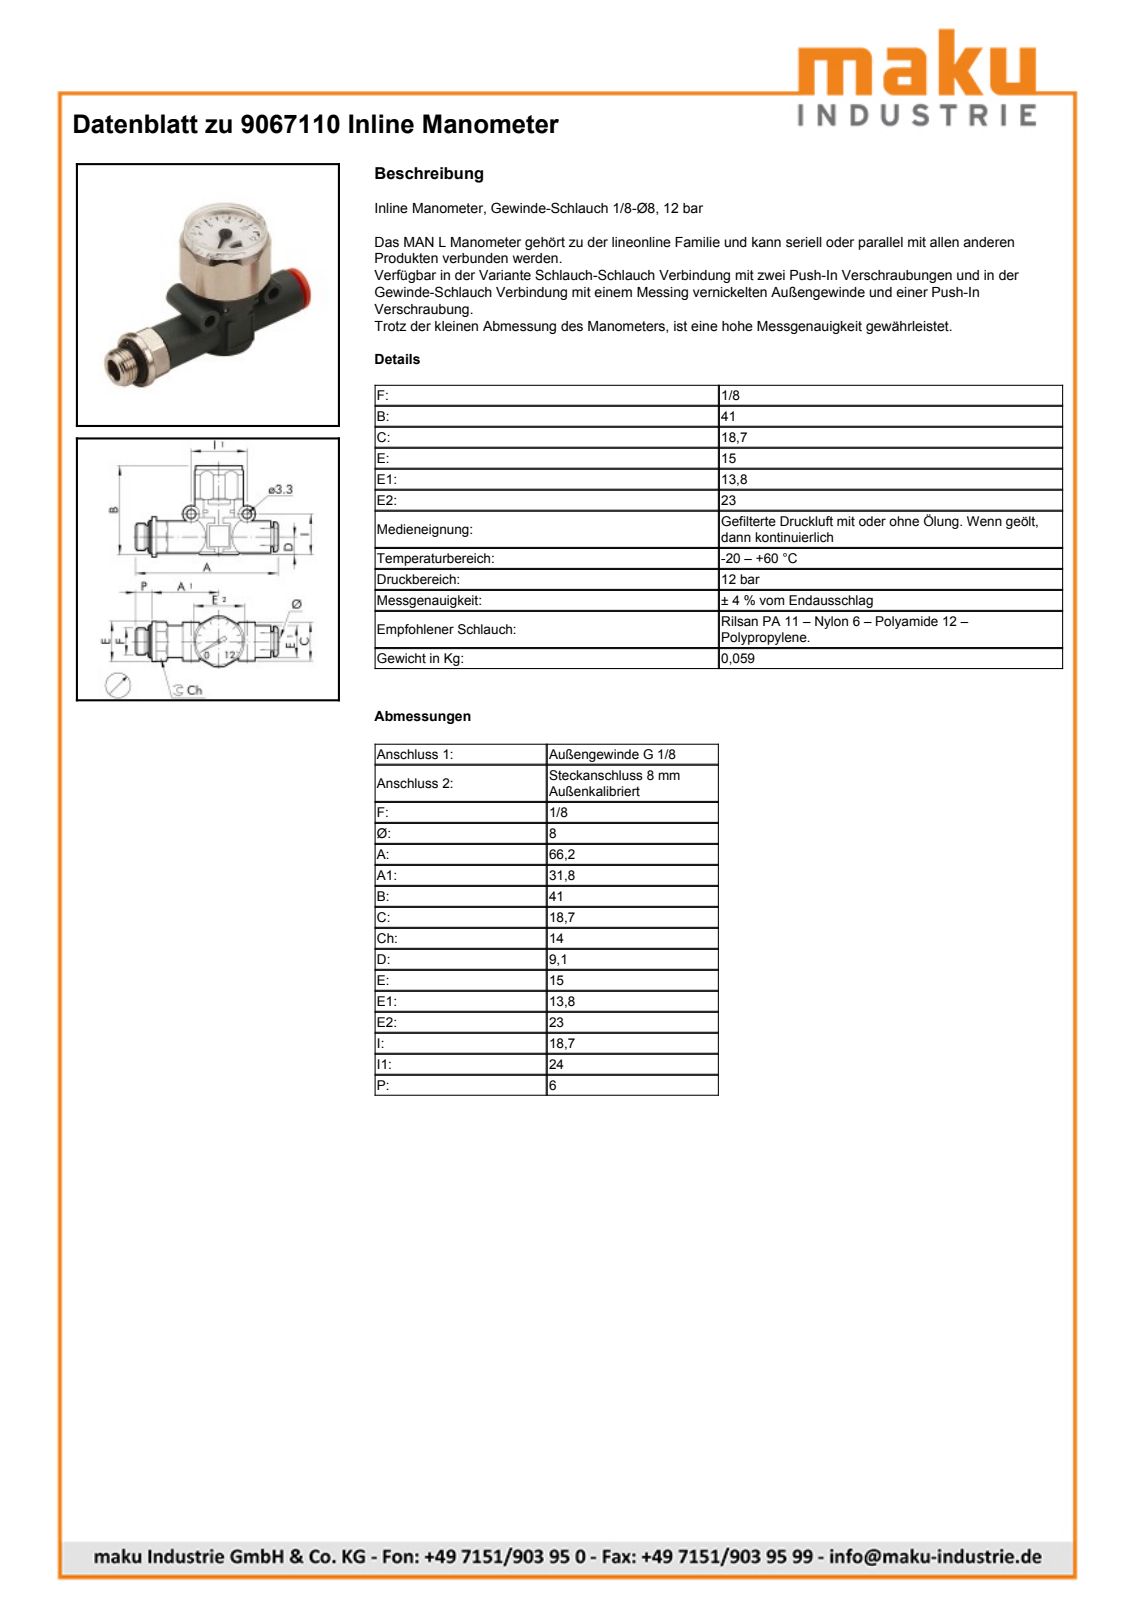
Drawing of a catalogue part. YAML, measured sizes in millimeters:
part_name: "9067110; LINE-ON-LINE D8 V2v/V3V_L body; LINE-ON-LINE D8 VNR-L bushing; LINE-ON-LINE D8-1/8 MAN-L thread port (+1 more)"
step_written_by: "PARTsolutions (AUTOMOTIVE_DESIGN)"
units: millimeters
bodies: {solids: 4, faces: 221, planar: 149, cylindrical: 60, other: 12}
overall_size: [66.4, 41.1, 22]
volume: 14367
surface_area: 10686
round_holes:
  - {diameter: 3.3, count: 2}
  - {diameter: 6, count: 2}
  - {diameter: 5, count: 1}
  - {diameter: 5.5, count: 1}
  - {diameter: 8.1, count: 1}
  - {diameter: 11, count: 1}
  - {diameter: 11.65, count: 1}
  - {diameter: 12.5, count: 1}
  - {diameter: 15, count: 1}
  - {diameter: 17.61, count: 1}
  - {diameter: 18.86, count: 1}
round_bosses_or_shafts:
  - {diameter: 6, count: 2}
  - {diameter: 20.96, count: 1}
  - {diameter: 18.8, count: 1}
  - {diameter: 17.91, count: 1}
  - {diameter: 15, count: 1}
  - {diameter: 13.8, count: 1}
  - {diameter: 13.6, count: 1}
  - {diameter: 9.73, count: 1}
partial_cylinders:
  - {radius: 0.71, count: 1}
  - {radius: 3.75, count: 1}
  - {radius: 7.75, count: 1}
  - {radius: 10.2, count: 1}
  - {radius: 10.35, count: 1}
  - {radius: 11.45, count: 1}
  - {radius: 11.5, count: 1}
face_to_face_distances: [20, 16.62, 22, 0.75, 21.25, 24.1, 40.72, 2, 4.1, 36.62]
hole_center_spacings: [15.37, 24]
